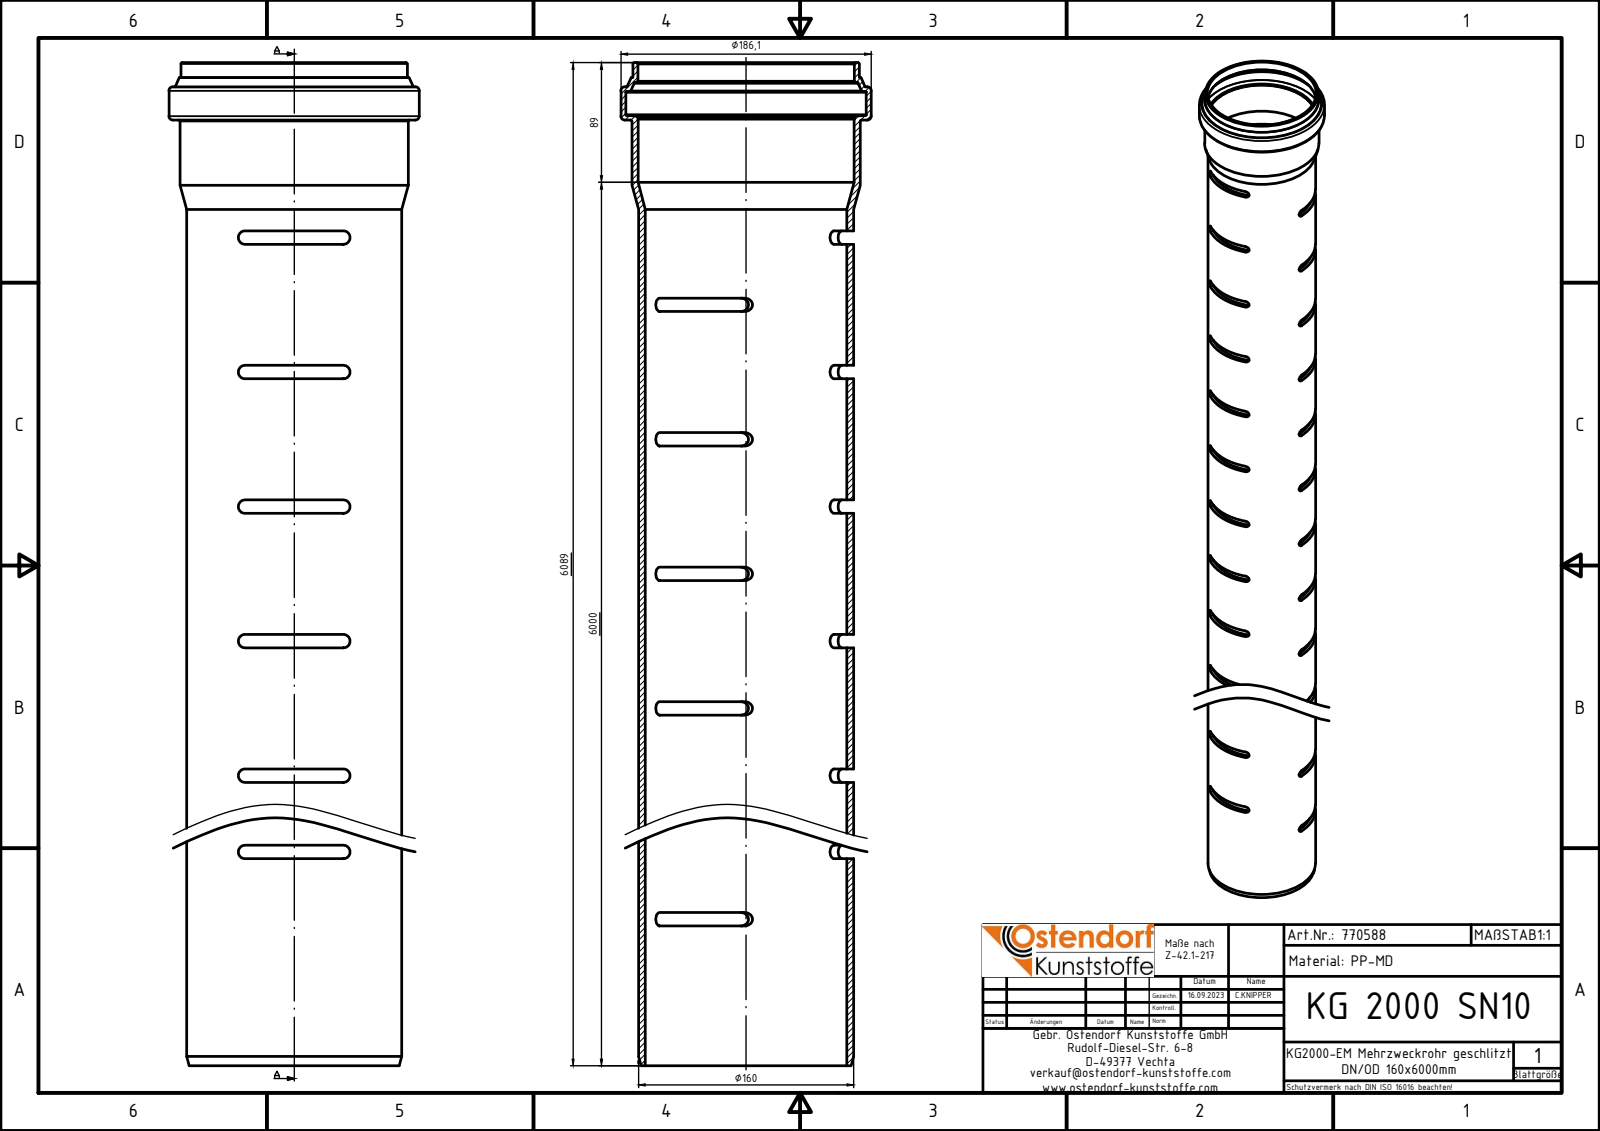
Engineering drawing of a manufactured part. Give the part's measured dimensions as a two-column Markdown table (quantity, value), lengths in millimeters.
| quantity | value |
| --- | --- |
| part name | 770588z |
| STEP written by | Autodesk Inventor 2024 (AUTOMOTIVE_DESIGN) |
| units | millimeters |
| bodies | 1 solid, 509 faces (242 planar, 245 cylindrical, 22 other) |
| overall size | 6089 × 186.1 × 186.1 |
| volume | 14 520 000 mm³ |
| surface area | 5 865 000 mm² |
| round holes (diameter × count) | 149.85 × 1, 160.6 × 1, 161 × 1, 178.7 × 1 |
| round bosses / shafts (diameter × count) | 186.1 × 1, 169.6 × 1, 168.4 × 1, 160 × 1 |
| partial cylindrical surfaces (radius × count) | 5 × 236 |
| main face-to-face distances | 100, 200, 300, 400, 500, 600, 700, 800, 900, 1000 |
